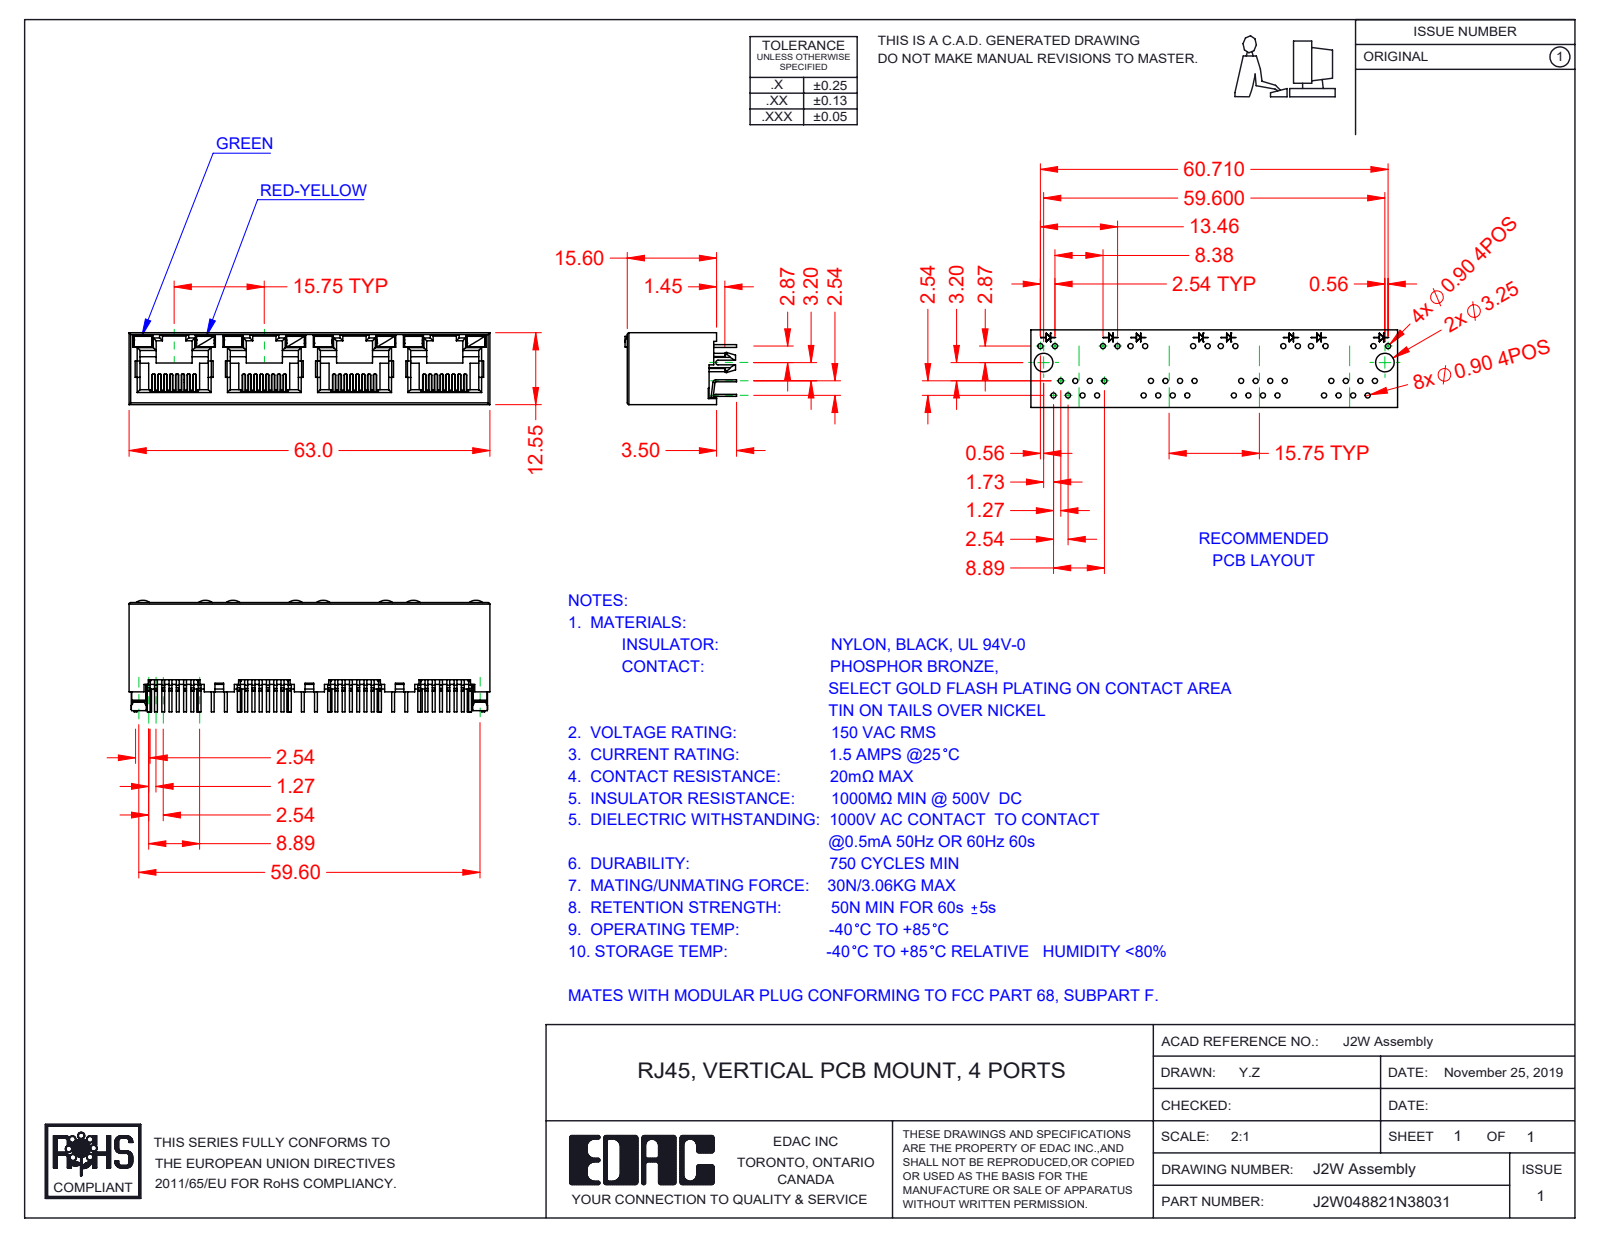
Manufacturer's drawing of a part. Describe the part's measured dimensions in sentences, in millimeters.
The part is named "J2W048821N38031; 2W Contact Lock; 2W LED LH_3-Green; 2W LED RH_8-Red-Yellow (+2 more)". Its 3-D file was written by "SolidWorks 2020 (CONFIG_CONTROL_DESIGN)". It is 45 solids with 3139 faces: 2600 planar, 481 cylindrical and 58 other. Overall it measures 63 by 19.5 by 12.55 millimeters. Its volume is 5 335 cubic millimeters and its surface area 13 144 square millimeters. Partial cylindrical surfaces (rounded edges, fillets, slot ends): 64 of radius 0.15, 29 of radius 0.2, 28 of radius 0.5, 14 of radius 0.3, 8 of radius 0.45, 8 of radius 2, 2 of radius 0.25, 2 of radius 1.5. The main face-to-face distances are 12.55, 11.9, 0.65, 15.75, 0.36, 1.5, 0.78, 0.6, 11.3, 31.5.
